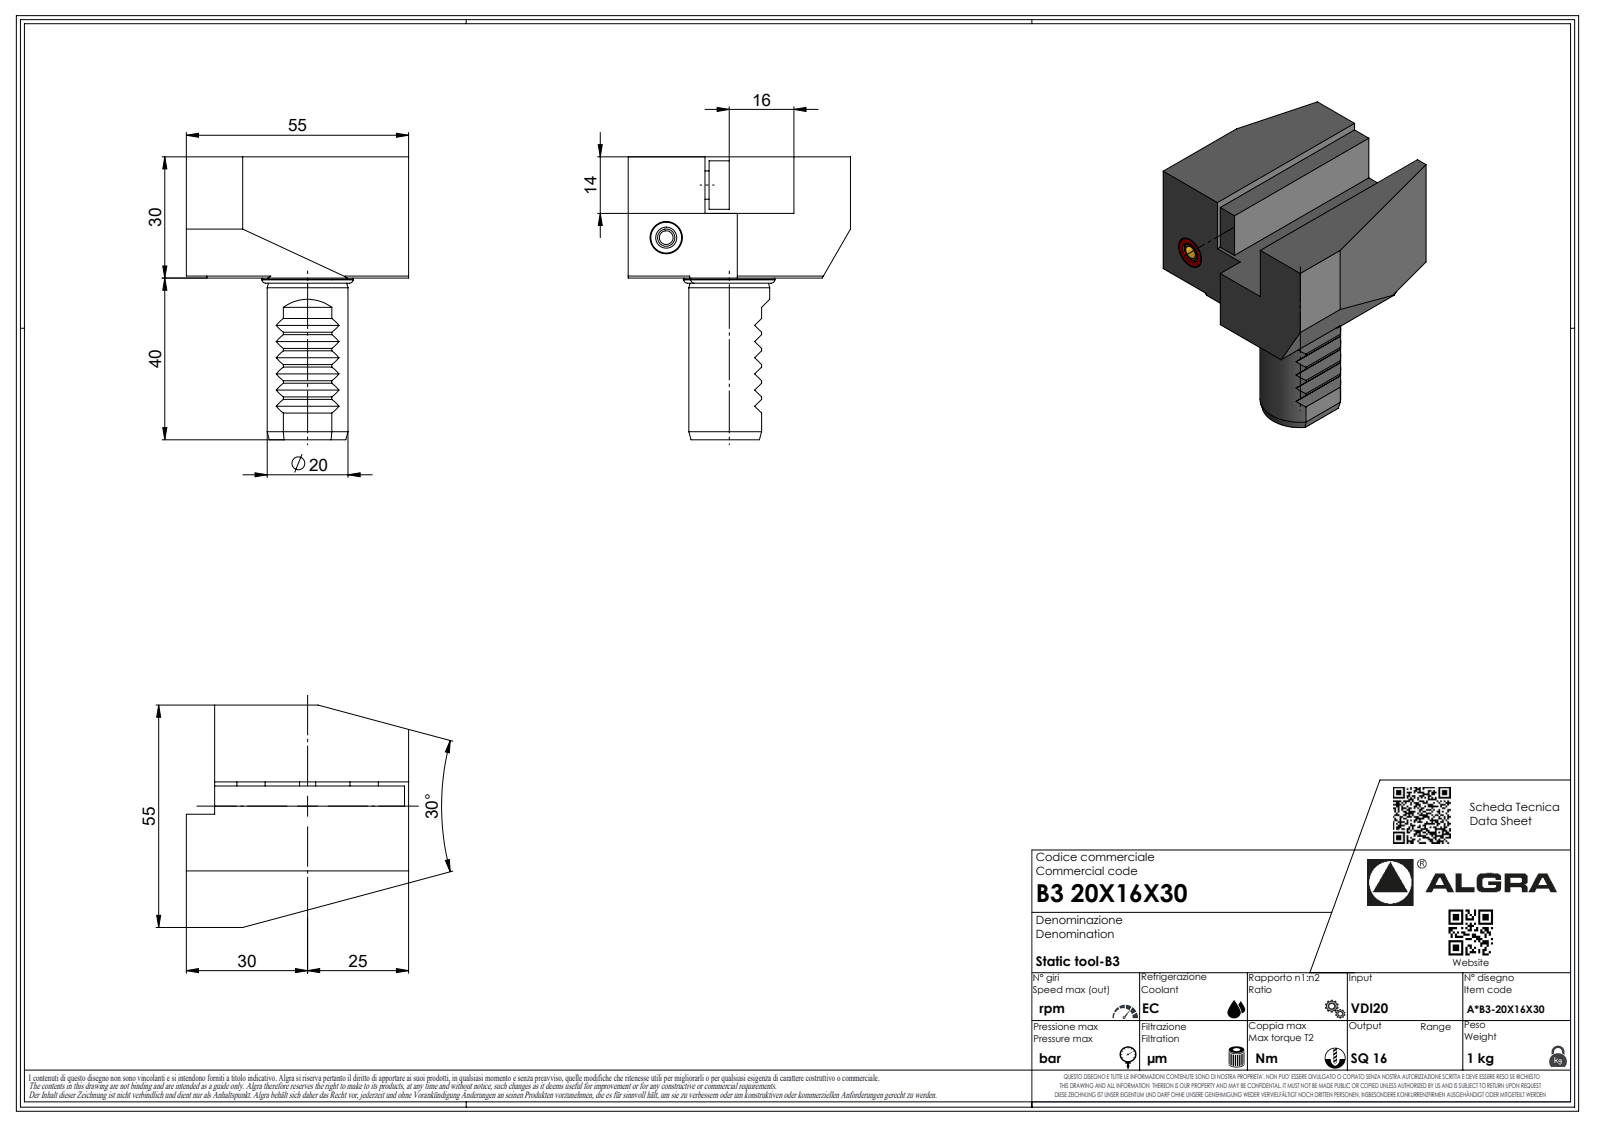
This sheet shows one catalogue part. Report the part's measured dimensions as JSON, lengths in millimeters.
{"part_name": "B320X16X30", "step_written_by": "SolidWorks 2023 (AUTOMOTIVE_DESIGN)", "units": "millimeters", "bodies": {"solids": 1, "faces": 320, "planar": 206, "cylindrical": 31, "other": 83}, "overall_size": [70, 55, 55], "volume_mm3": 74140, "surface_area_mm2": 15275, "round_holes": [[2.1, 1]], "round_bosses_or_shafts": [[22.72, 1], [20, 1], [6.37, 1], [1.7, 1]], "partial_cylinders_radius": [[0.33, 7], [0.52, 7], [3.7, 7], [0.21, 1], [25, 1]], "face_to_face_distances": [16, 30, 14, 55, 48, 41, 1, 7, 13, 25]}
